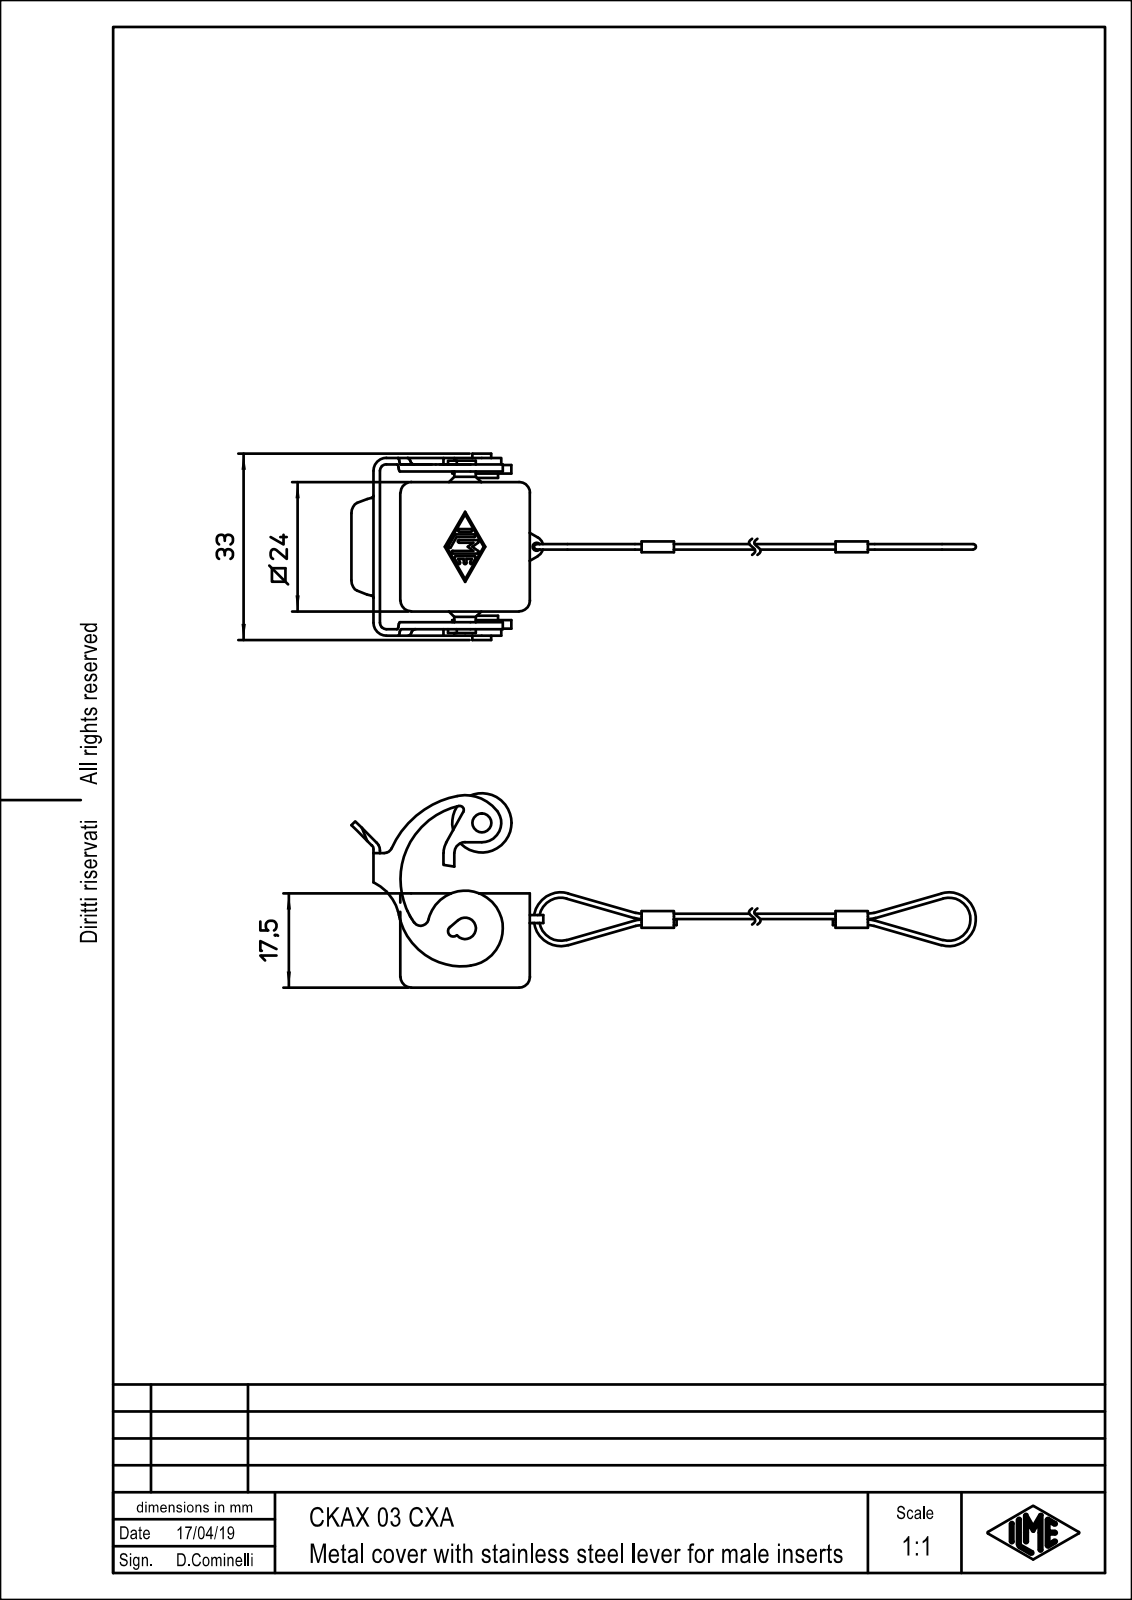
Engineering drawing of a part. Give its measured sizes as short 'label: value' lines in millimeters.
name: CKAX_03_CXA
written by: PTC Creo Elements/Direct Modeling 19.0E 27-Jun-2016 (C) Parametric Technology GmbH (AUTOMOTIVE_DESIGN)
unit: mm
bodies: 1 solid, 200 faces (72 planar, 104 cylindrical, 24 other)
size: 116 × 36.1 × 34.6
volume: 4 905 mm³; area: 7 361 mm²
holes: 1× ⌀1.5
bosses: 6× ⌀1, 1× ⌀11, 1× ⌀6, 1× ⌀4, 1× ⌀3.5, 1× ⌀3.2
rounds: 15× R2, 10× R1.2, 8× R0.5, 4× R1, 2× R1.5, 2× R2.4, 1× R0.75, 1× R3.6
face distances: 1.5, 22.5, 2, 1.2, 21, 24, 4.8, 25.8, 3.3, 27.3
